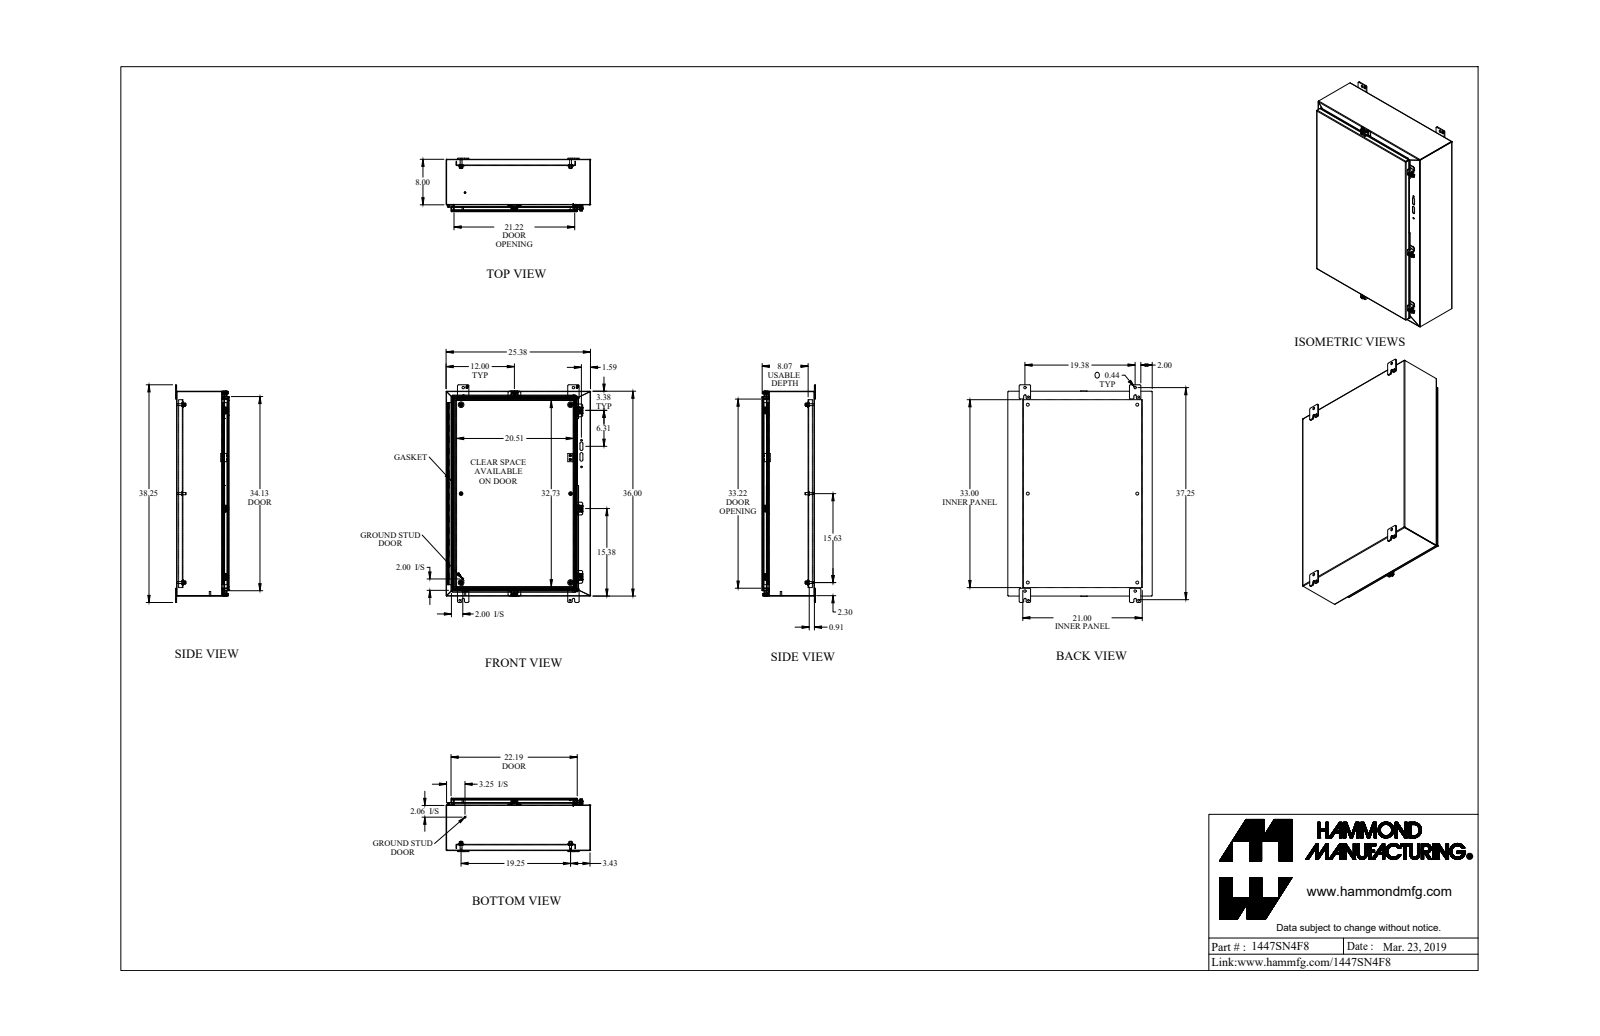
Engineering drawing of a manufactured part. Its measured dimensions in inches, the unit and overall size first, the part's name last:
Units: inches
Overall size (bounding box): 38.25 × 25.375 × 9.397
Round holes (diameter × count): ⌀0.313 ×6, ⌀0.5 ×6, ⌀0.213 ×5, ⌀0.265 ×5, ⌀0.375 ×5, ⌀0.307 ×4, ⌀0.437 ×4, ⌀0.445 ×4, ⌀0.15 ×2, ⌀0.156 ×2, ⌀0.281 ×2, ⌀0.187 ×1
Round bosses / shafts (diameter × count): ⌀0.65 ×6, ⌀0.375 ×6, ⌀0.33 ×6, ⌀0.5 ×5, ⌀0.39 ×5, ⌀0.244 ×5, ⌀1 ×4, ⌀0.25 ×4
Partial cylindrical surfaces — rounded edges, fillets, slot ends (radius × count): R0.25 ×28, R0.048 ×27, R0.143 ×27, R0.188 ×24, R0.036 ×23, R0.108 ×23, R0.045 ×10, R0.141 ×10
Main face-to-face distances: 0.072, 9.066, 9.138, 0.072, 9.138, 9.21, 0.095, 8.106, 8.034, 1.032
Hole centre spacings: 15.625, 19.375, 24.793, 2.122, 12.155, 19.25, 21.146, 1.735
Volume: 312.7 in³ · Surface area: 8 171 in²
Bodies: 52 solids, 1764 faces (1024 planar, 630 cylindrical, 110 other)
Part name (STEP PRODUCT): 1447SN4F8_Default
STEP written by: SolidWorks 2019 (CONFIG_CONTROL_DESIGN)
